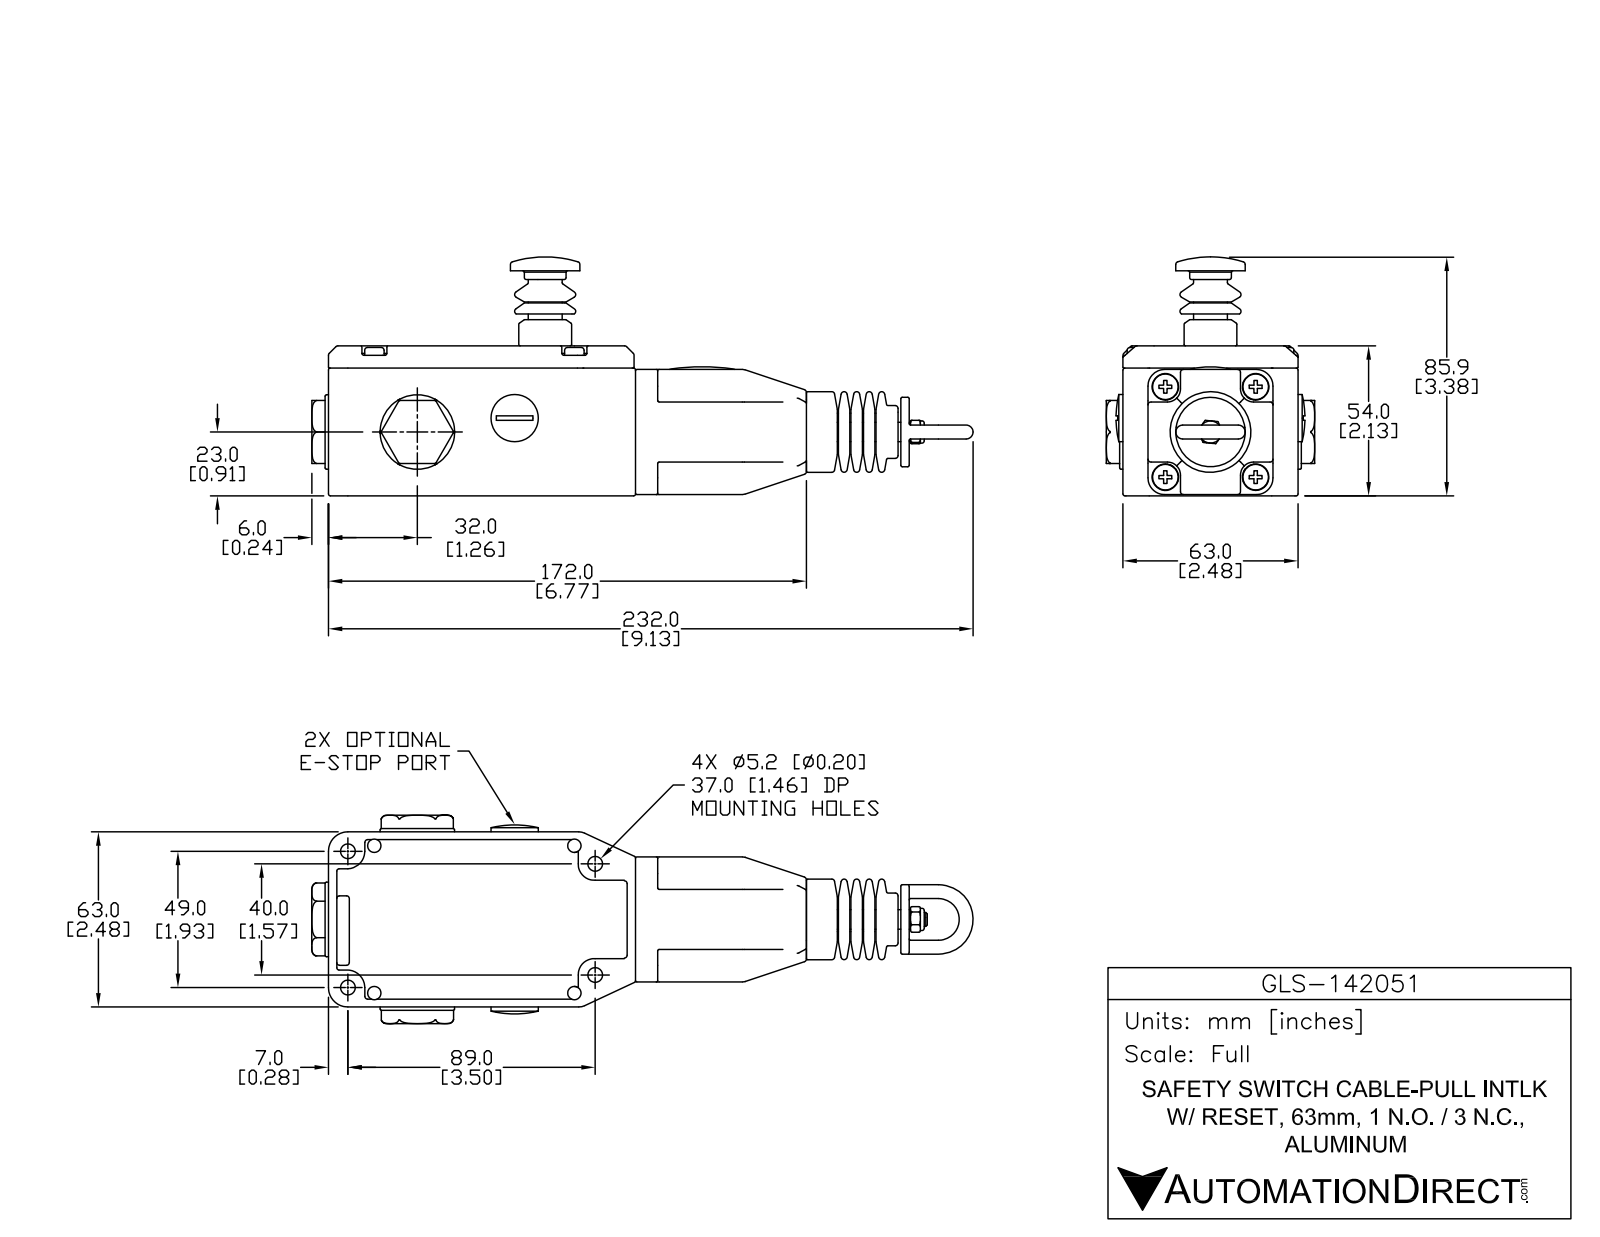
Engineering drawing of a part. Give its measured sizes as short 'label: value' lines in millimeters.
name: GLS-142051
written by: SolidWorks 2013 (AUTOMOTIVE_DESIGN)
unit: mm
bodies: 1 solid, 565 faces (188 planar, 183 cylindrical, 194 other)
size: 239.16 × 86 × 75.6
volume: 482 310 mm³; area: 58 090 mm²
holes: 4× ⌀4.75, 4× ⌀5, 4× ⌀9.5
bosses: 4× ⌀9.2, 4× ⌀6, 2× ⌀26.8, 2× ⌀25, 2× ⌀19, 2× ⌀5, 1× ⌀29, 1× ⌀17
rounds: 42× R0.5, 20× R0.75, 4× R4, 4× R4.5, 4× R4.8, 4× R16, 2× R7, 2× R8.2
face distances: 54, 63, 9, 11.7, 33.3, 4.5, 49.5, 45, 27, 16.2
hole spacings: 9.6, 9.62, 32.4, 32.6, 45.96, 46.61, 51.39, 52
